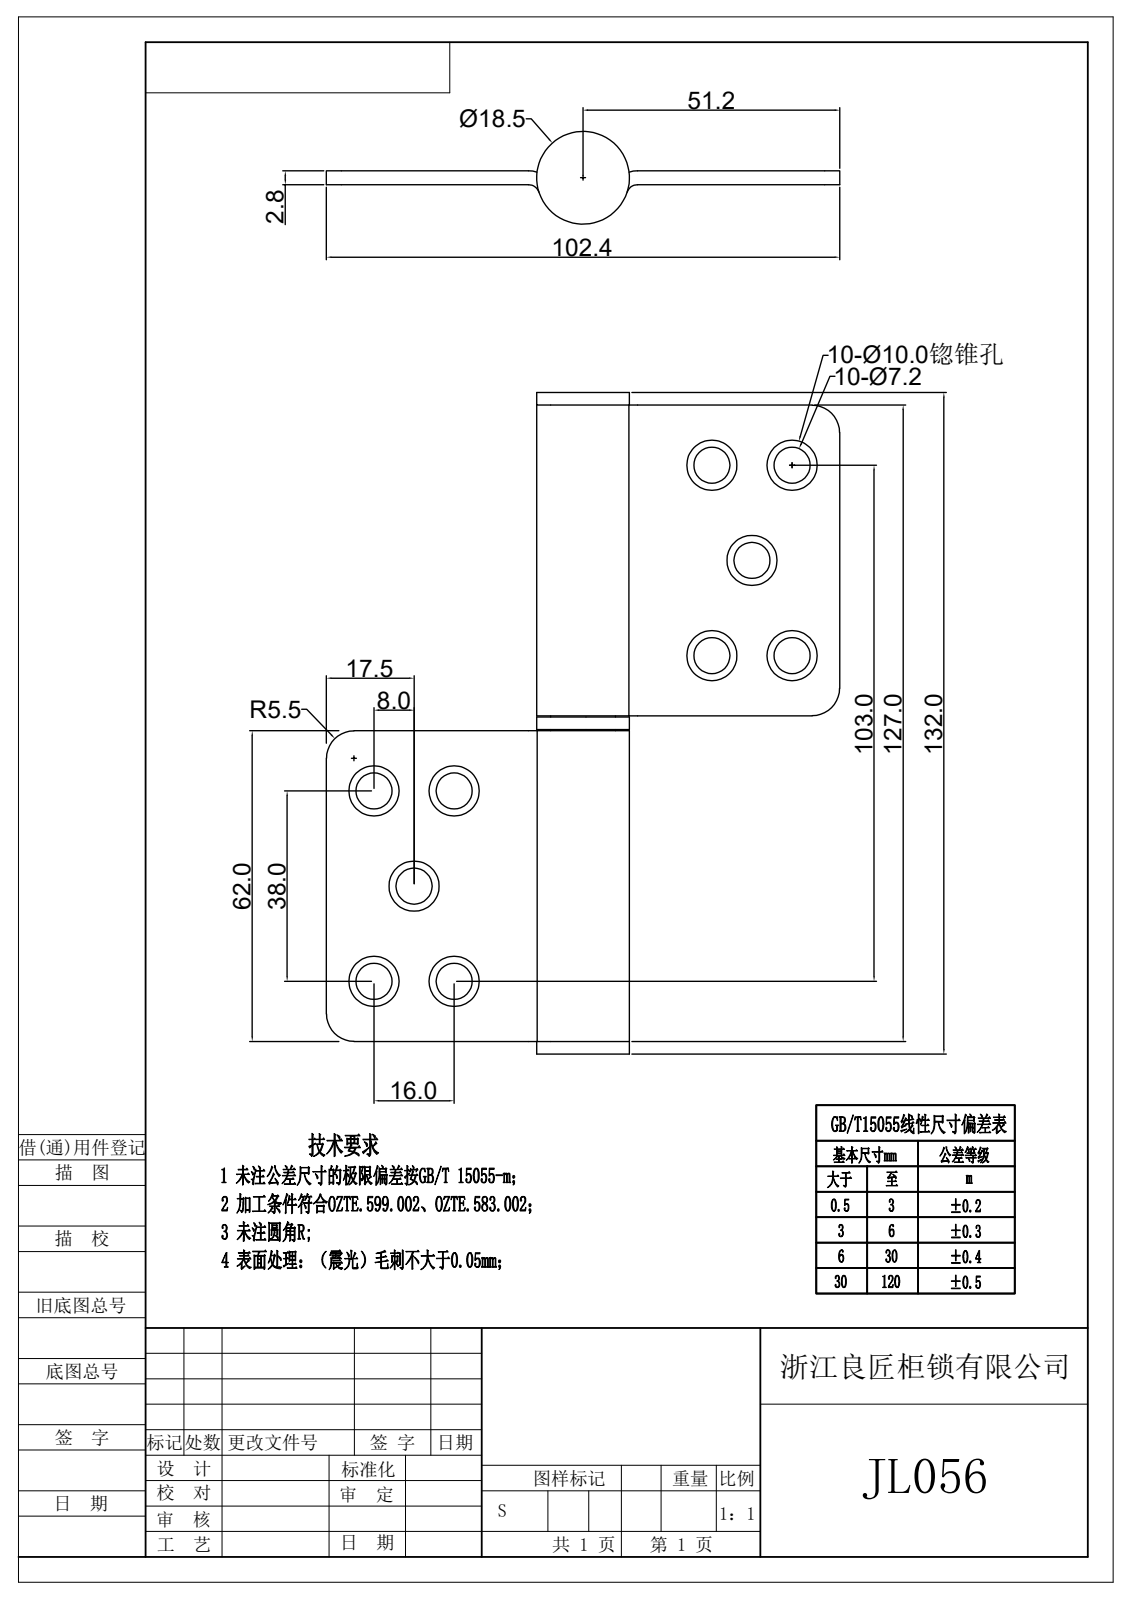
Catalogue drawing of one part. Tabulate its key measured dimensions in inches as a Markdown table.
| quantity | value |
| --- | --- |
| STEP written by | Rhino 8.5 (CONFIG_CONTROL_DESIGN) |
| units | inches |
| bodies | 5 solids, 112 faces (22 planar, 48 cylindrical, 42 other) |
| overall size | 5.197 × 4.031 × 0.728 |
| volume | 2.94 in³ |
| surface area | 47.84 in² |
| round holes (diameter × count) | 0.283 × 10, 0.236 × 1, 0.508 × 1 |
| round bosses / shafts (diameter × count) | 0.728 × 1 |
| partial cylindrical surfaces (radius × count) | 0.118 × 4, 0.087 × 2, 0.197 × 2 |
| main face-to-face distances | 0.11, 0.098, 2.549, 5.098, 2.539, 2.657, 2.441, 2.559, 5, 2.648 |
| hole center spacings | 0.812, 3.687, 0.63, 1.496, 1.623, 2.859, 2.958, 3.263 |
